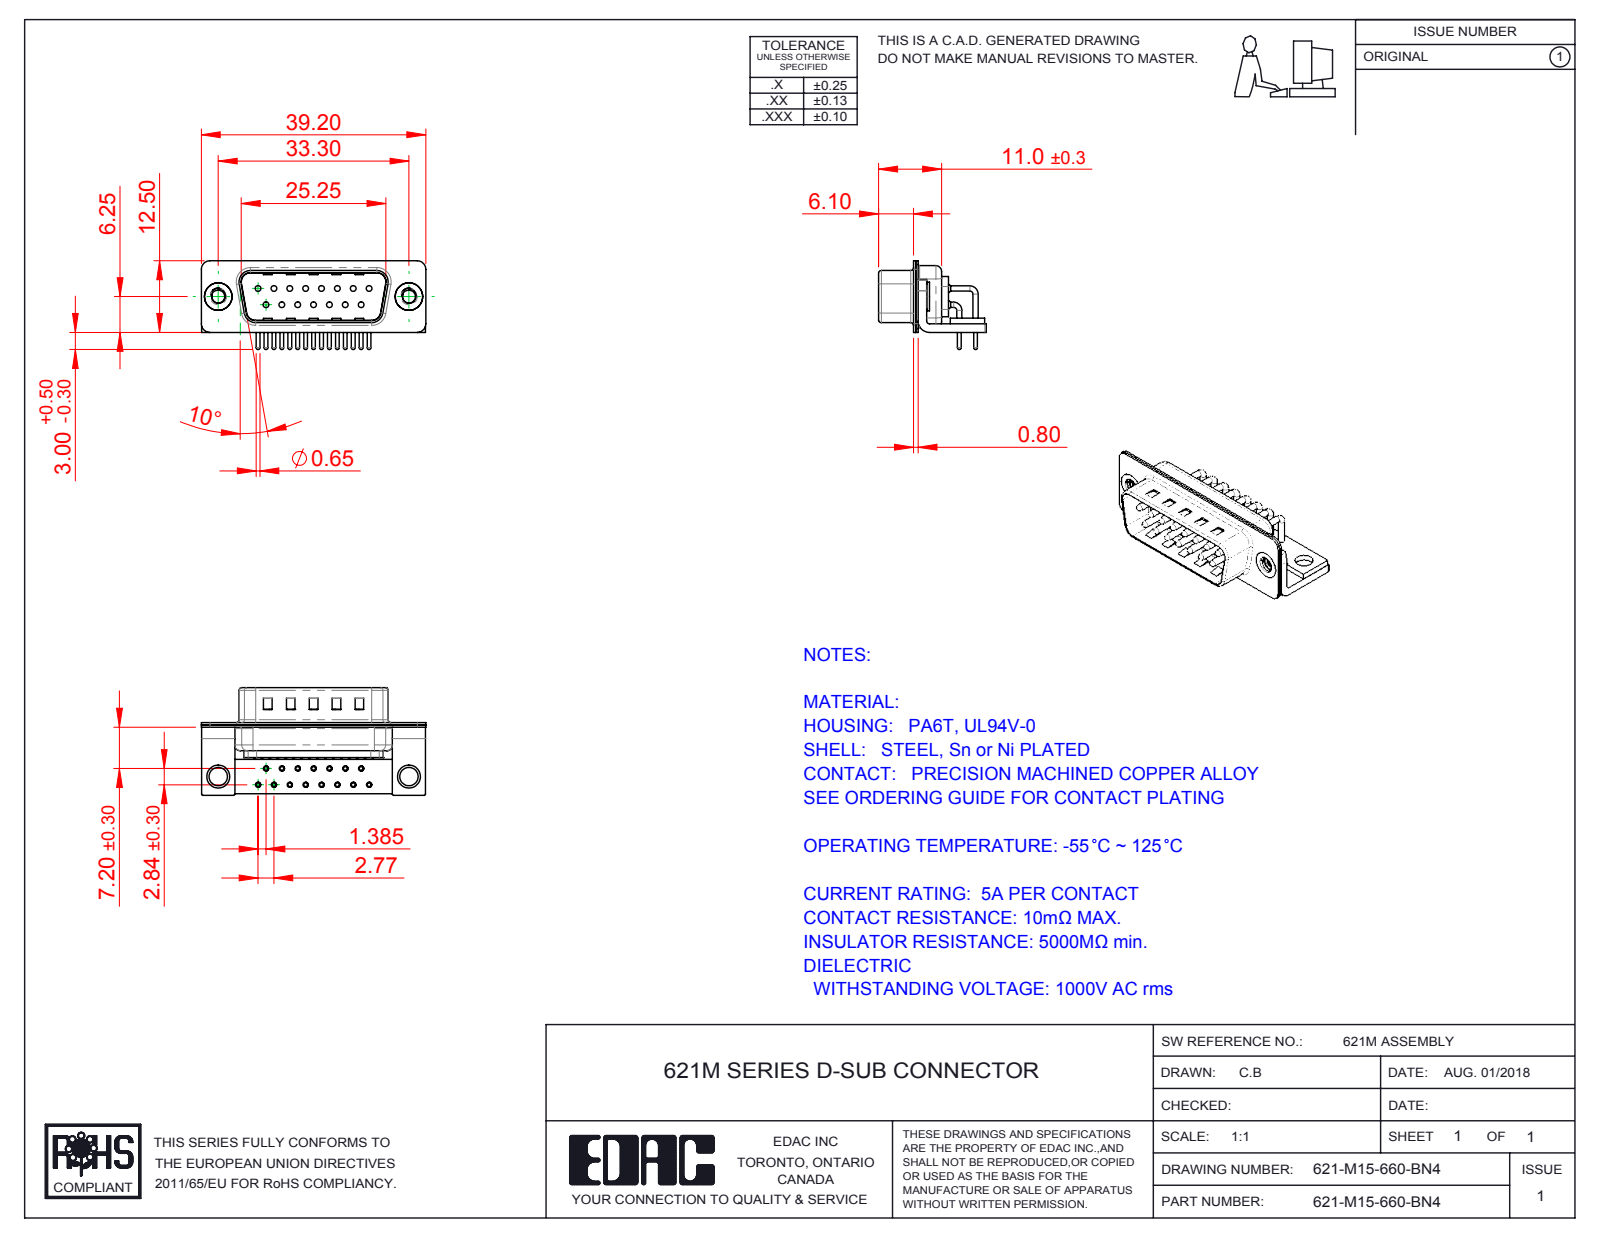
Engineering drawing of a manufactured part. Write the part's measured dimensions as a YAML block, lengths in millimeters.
part_name: "621M 4-40 Threaded Rivet_Stabilizer; 621M Stabilizer Board_15 Contacts; 621M Housing_15 Contacts; 621M Shell Rear_15 Contacts (+5 more)"
step_written_by: "SolidWorks 2016 (CONFIG_CONTROL_DESIGN)"
units: millimeters
bodies: {solids: 23, faces: 2070, planar: 1125, cylindrical: 725, other: 220}
overall_size: [39.2, 18.8, 15.49]
volume: 2371
surface_area: 6349
round_holes:
  - {diameter: 0.9, count: 15}
  - {diameter: 1, count: 15}
  - {diameter: 1.7, count: 15}
  - {diameter: 2, count: 15}
  - {diameter: 2.26, count: 2}
  - {diameter: 3.2, count: 2}
  - {diameter: 4, count: 2}
  - {diameter: 4.8, count: 2}
round_bosses_or_shafts:
  - {diameter: 0.9, count: 22}
  - {diameter: 1.5, count: 15}
  - {diameter: 0.65, count: 15}
  - {diameter: 5, count: 2}
  - {diameter: 4.9, count: 2}
partial_cylinders:
  - {radius: 0.25, count: 16}
  - {radius: 1.5, count: 16}
  - {radius: 1.01, count: 15}
  - {radius: 2, count: 13}
  - {radius: 0.5, count: 9}
  - {radius: 1.6, count: 8}
  - {radius: 0.6, count: 4}
  - {radius: 0.65, count: 4}
face_to_face_distances: [0.4, 0.85, 1.5, 0.8, 1.25, 10.4, 9.55, 1, 2.1, 1.9]
hole_center_spacings: [3.16, 2.77, 5.54, 8.31, 11.08, 5.03, 5.04, 7.48]
